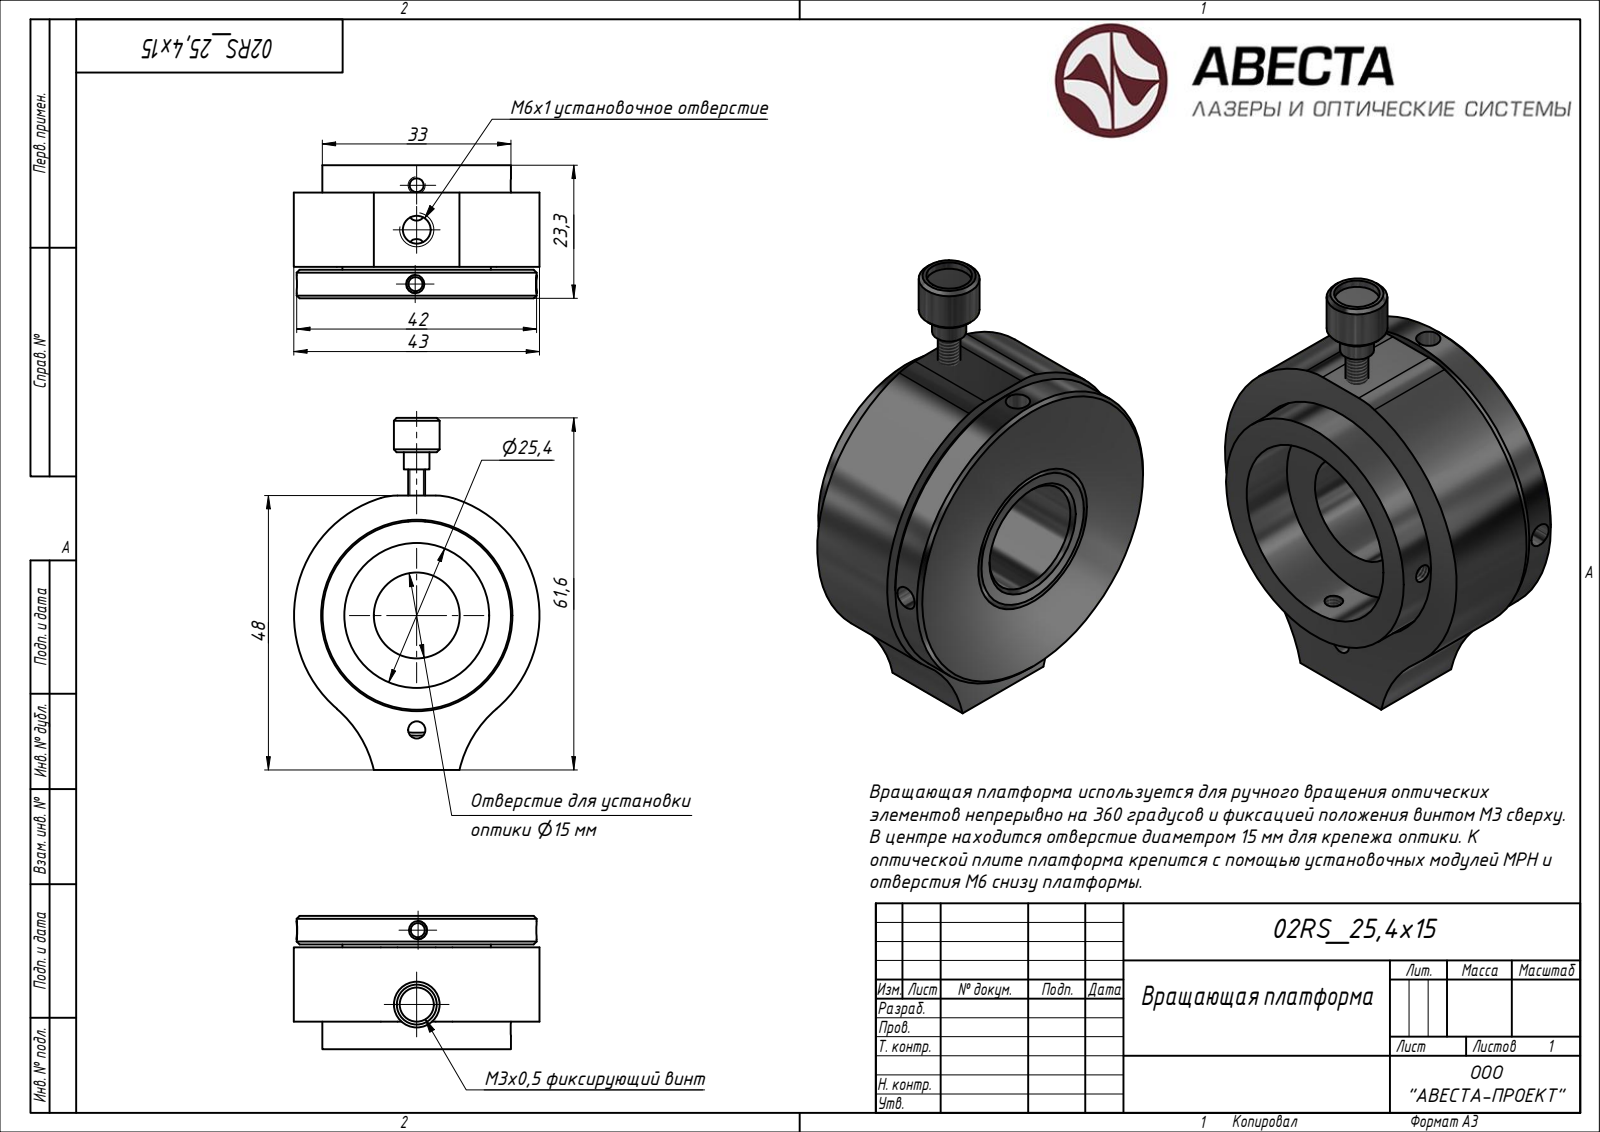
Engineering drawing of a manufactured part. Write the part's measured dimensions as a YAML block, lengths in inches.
part_name: "02-RS-254x15-Shell"
step_written_by: "Autodesk Inventor 2019 (AUTOMOTIVE_DESIGN)"
units: inches
bodies: {solids: 1, faces: 72, planar: 22, cylindrical: 38, other: 12}
overall_size: [2.424, 1.693, 0.917]
volume: 1.487
surface_area: 18.36
round_holes:
  - {diameter: 0.098, count: 4}
  - {diameter: 0.126, count: 4}
  - {diameter: 0.097, count: 2}
  - {diameter: 0.118, count: 1}
  - {diameter: 0.193, count: 1}
  - {diameter: 0.236, count: 1}
  - {diameter: 0.591, count: 1}
  - {diameter: 1, count: 1}
  - {diameter: 1.102, count: 1}
  - {diameter: 1.26, count: 1}
  - {diameter: 1.319, count: 1}
round_bosses_or_shafts:
  - {diameter: 1.654, count: 1}
  - {diameter: 1.299, count: 1}
  - {diameter: 1.024, count: 1}
  - {diameter: 0.945, count: 1}
  - {diameter: 0.315, count: 1}
  - {diameter: 0.177, count: 1}
  - {diameter: 0.118, count: 1}
partial_cylinders:
  - {radius: 0.394, count: 3}
  - {radius: 0.787, count: 2}
  - {radius: 0.846, count: 1}
face_to_face_distances: [0.197, 0.217, 0.531, 0.02, 0.512, 0.728, 0.295, 0.425, 0.185, 0.327]
hole_center_spacings: [0.138, 0.169, 0.307, 0.787]
